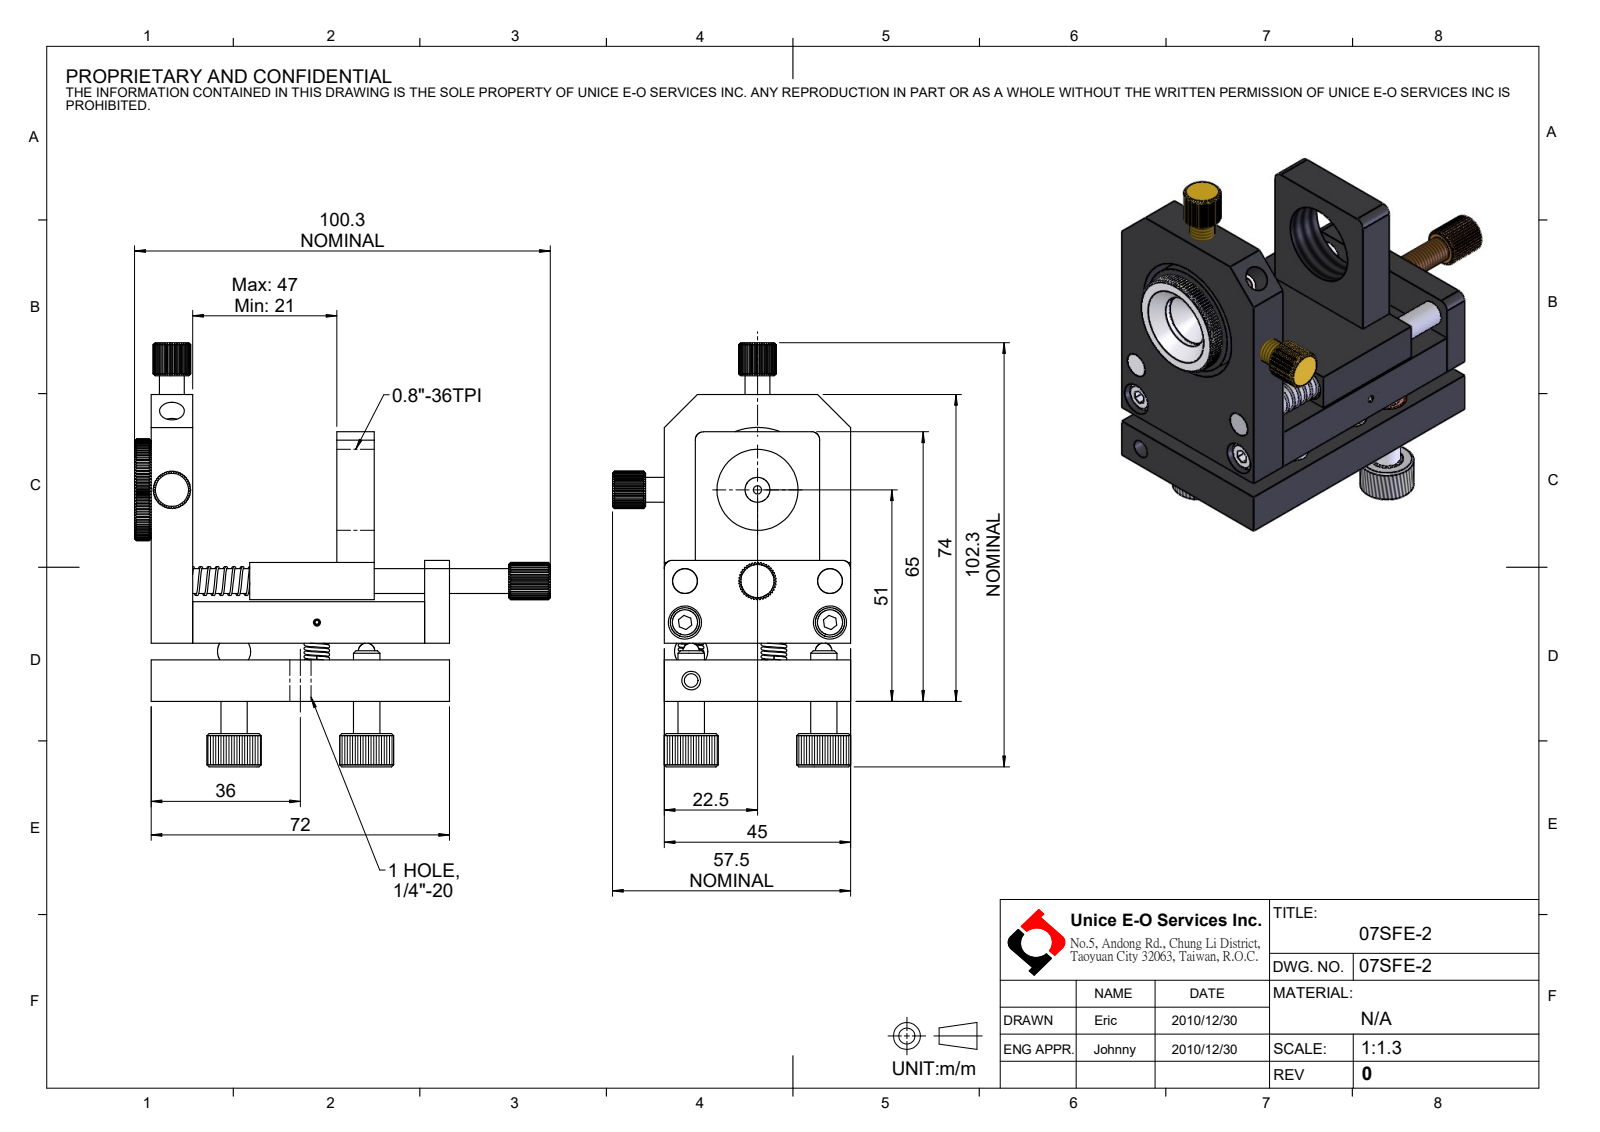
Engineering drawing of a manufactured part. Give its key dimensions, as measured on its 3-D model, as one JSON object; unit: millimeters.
{"part_name": "07SFE-2", "step_written_by": "SolidWorks 2016 (CONFIG_CONTROL_DESIGN)", "units": "millimeters", "bodies": {"solids": 40, "faces": 1874, "planar": 647, "cylindrical": 462, "other": 765}, "overall_size": [102.3, 100.3, 57.5], "volume_mm3": 107068, "surface_area_mm2": 56168, "round_holes": [[3.3, 6], [4.5, 6], [8, 6], [6, 5], [1, 4], [4, 3], [5, 3], [1.7, 2], [5.11, 2], [7, 2], [7.9, 2], [9.5, 2]], "round_bosses_or_shafts": [[6, 4], [1.3, 4], [0.8, 4], [13, 2], [8, 2], [7, 2], [6.35, 2], [4, 2]], "partial_cylinders_radius": [[0.75, 4], [1, 4], [2, 4], [4.5, 3], [1.5, 1], [12.25, 1]], "face_to_face_distances": [10, 14, 4, 24, 9, 45, 9.5, 66, 6, 19.5], "hole_center_spacings": [10, 15.52, 8.65, 10.77, 12, 14.08, 16, 16.49]}
